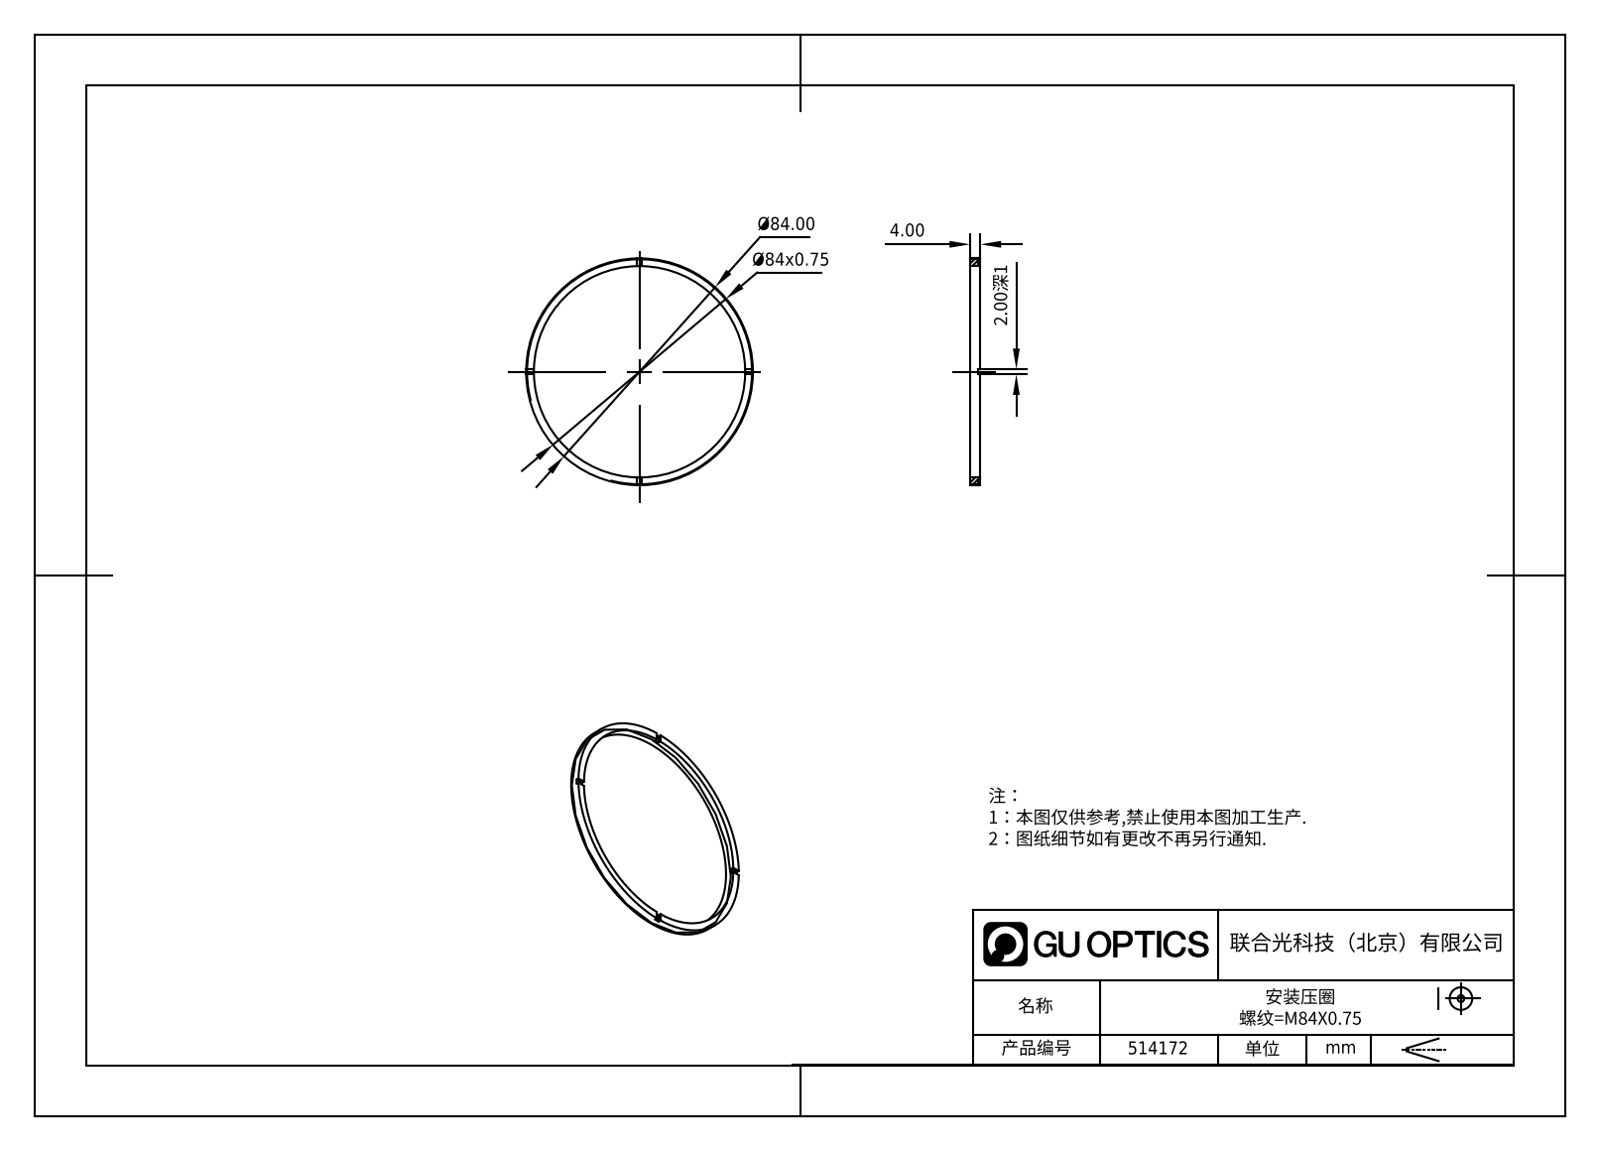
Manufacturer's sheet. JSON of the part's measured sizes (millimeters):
{"part_name": "514172", "step_written_by": "SolidWorks 2020 (CONFIG_CONTROL_DESIGN)", "units": "millimeters", "bodies": {"solids": 1, "faces": 21, "planar": 17, "cylindrical": 4, "other": 0}, "overall_size": [84, 84, 4.5], "volume_mm3": 3411, "surface_area_mm2": 3825, "round_holes": [[78, 1]], "round_bosses_or_shafts": [[84, 1]], "face_to_face_distances": [4.5, 3.5, 1, 2]}
